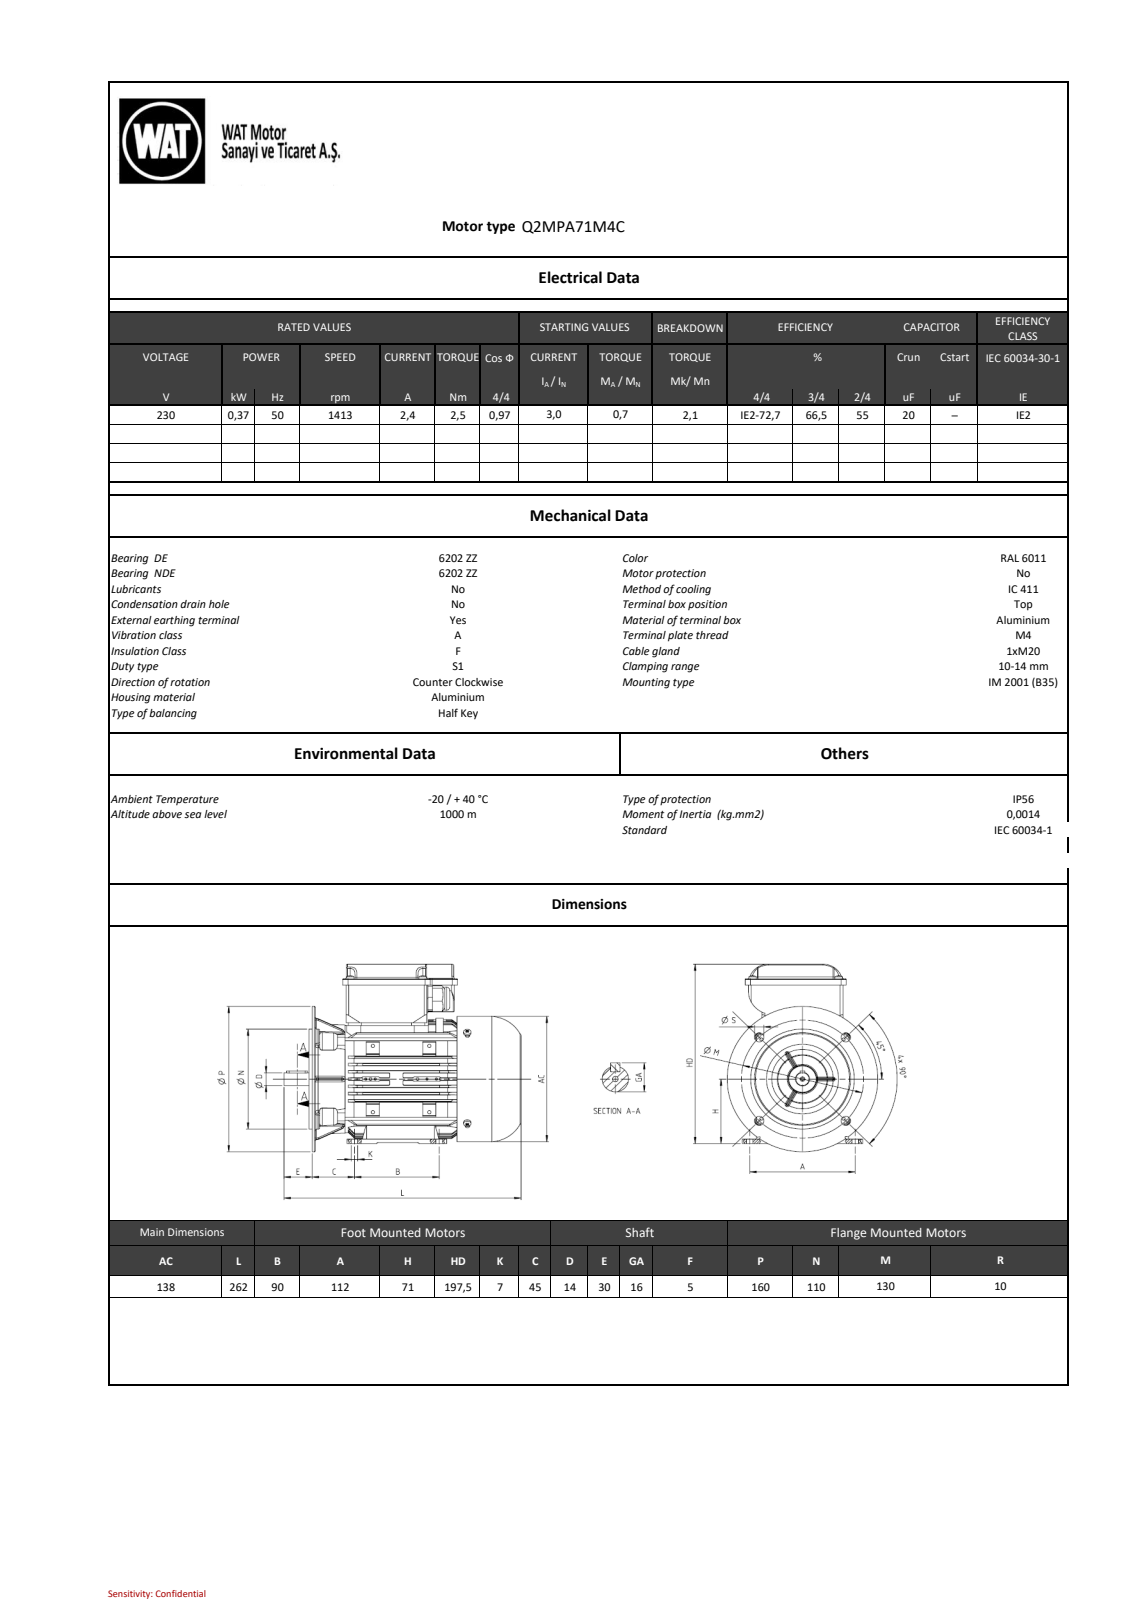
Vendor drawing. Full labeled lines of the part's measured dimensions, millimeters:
Part name (STEP PRODUCT): BY6434017xx_004-TK_QM63-80; BY6424130xx_004-TKK_QM63-80; BY6432282xx_005-MOTOR_KAPAGI_QS71FA_ISLEME_YENI; 641304741_AZ-KAMA PARALEL A 5x5x22 St50 DIN6885 (+8 more)
STEP written by: SIEMENS PLM Software NX2206.8101 (AUTOMOTIVE_DESIGN)
Units: millimetres
Bodies: 26 solids, 3060 faces (1314 planar, 853 cylindrical, 893 other)
Overall size (bounding box): 262 × 206.5 × 160
Volume: 835 645 mm³ · Surface area: 523 994 mm²
Round holes (diameter × count): ⌀3.3 ×9, ⌀3.65 ×8, ⌀4.5 ×8, ⌀2.5 ×6, ⌀4 ×4, ⌀4.65 ×4, ⌀4.8 ×4, ⌀5.2 ×4, ⌀7 ×4, ⌀10 ×4, ⌀3 ×3, ⌀3.7 ×3
Round bosses / shafts (diameter × count): ⌀8 ×8, ⌀4 ×8, ⌀3 ×8, ⌀160 ×1, ⌀138 ×1, ⌀110 ×1, ⌀26 ×1, ⌀25.28 ×1
Partial cylindrical surfaces — rounded edges, fillets, slot ends (radius × count): R1 ×171, R2 ×68, R0.5 ×38, R1.2 ×36, R10 ×32, R0.75 ×18, R5 ×18, R2.5 ×14
Main face-to-face distances: 3, 194.5, 5, 197.5, 2, 158.5, 1, 189.2, 194.2, 4
Hole centre spacings: 87.43, 89.67, 89.74, 55, 36.59, 65, 60, 3.13
